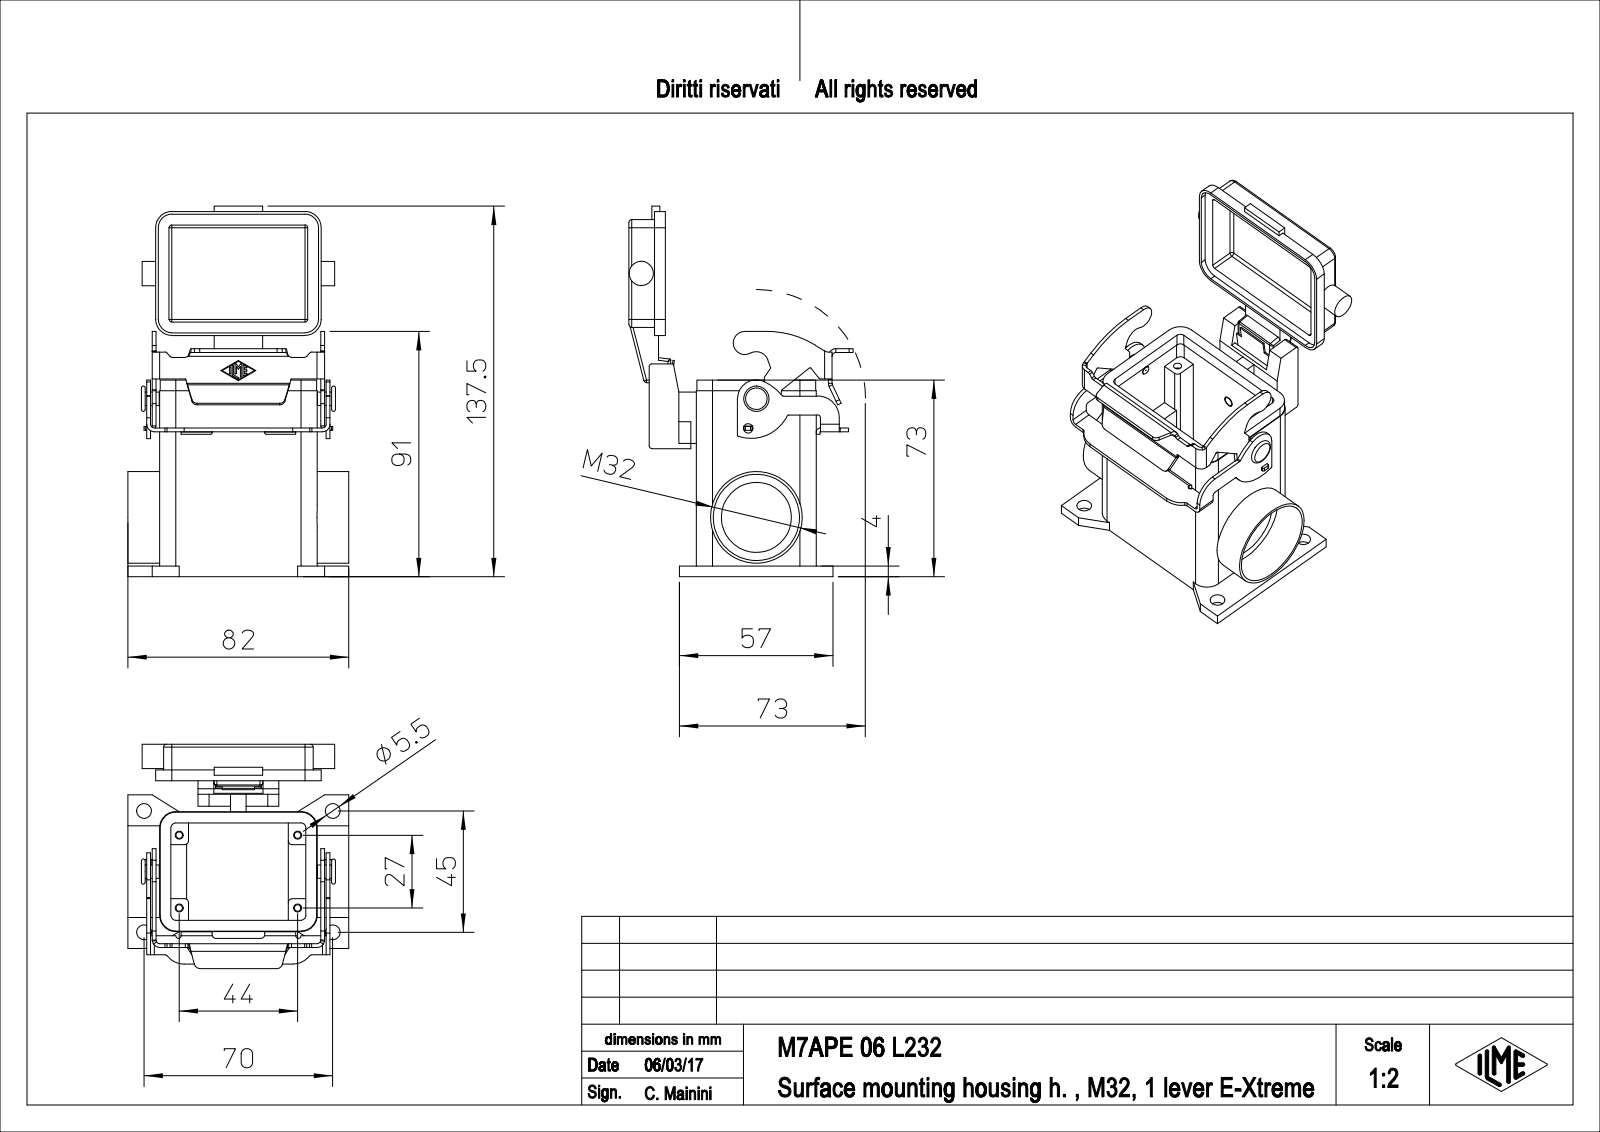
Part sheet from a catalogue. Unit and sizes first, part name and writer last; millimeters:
Units: millimetres
Overall size (bounding box): 137.5 × 83.23 × 82
Round holes (diameter × count): ⌀2.46 ×4, ⌀3 ×4, ⌀5.5 ×4, ⌀3.5 ×1, ⌀4 ×1, ⌀26 ×1, ⌀32 ×1
Round bosses / shafts (diameter × count): ⌀34 ×1, ⌀9 ×1, ⌀7 ×1, ⌀5 ×1, ⌀3.2 ×1, ⌀3 ×1
Partial cylindrical surfaces — rounded edges, fillets, slot ends (radius × count): R1 ×36, R0.25 ×16, R0.5 ×13, R1.5 ×11, R2 ×9, R6 ×8, R1.4 ×6, R2.8 ×6
Main face-to-face distances: 4, 40.5, 2, 1.4, 44.5, 13.5, 10.75, 36.5, 6.75, 68
Hole centre spacings: 15.81, 38.28, 57.71, 67.42, 27, 44, 45, 51.62
Volume: 103 899 mm³ · Surface area: 64 501 mm²
Bodies: 1 solid, 566 faces (293 planar, 233 cylindrical, 40 other)
Part name (STEP PRODUCT): M7APE_06_L232
STEP written by: PTC Creo Elements/Direct Modeling 19.0E 27-Jun-2016 (C) Parametric Technology GmbH (AUTOMOTIVE_DESIGN)
